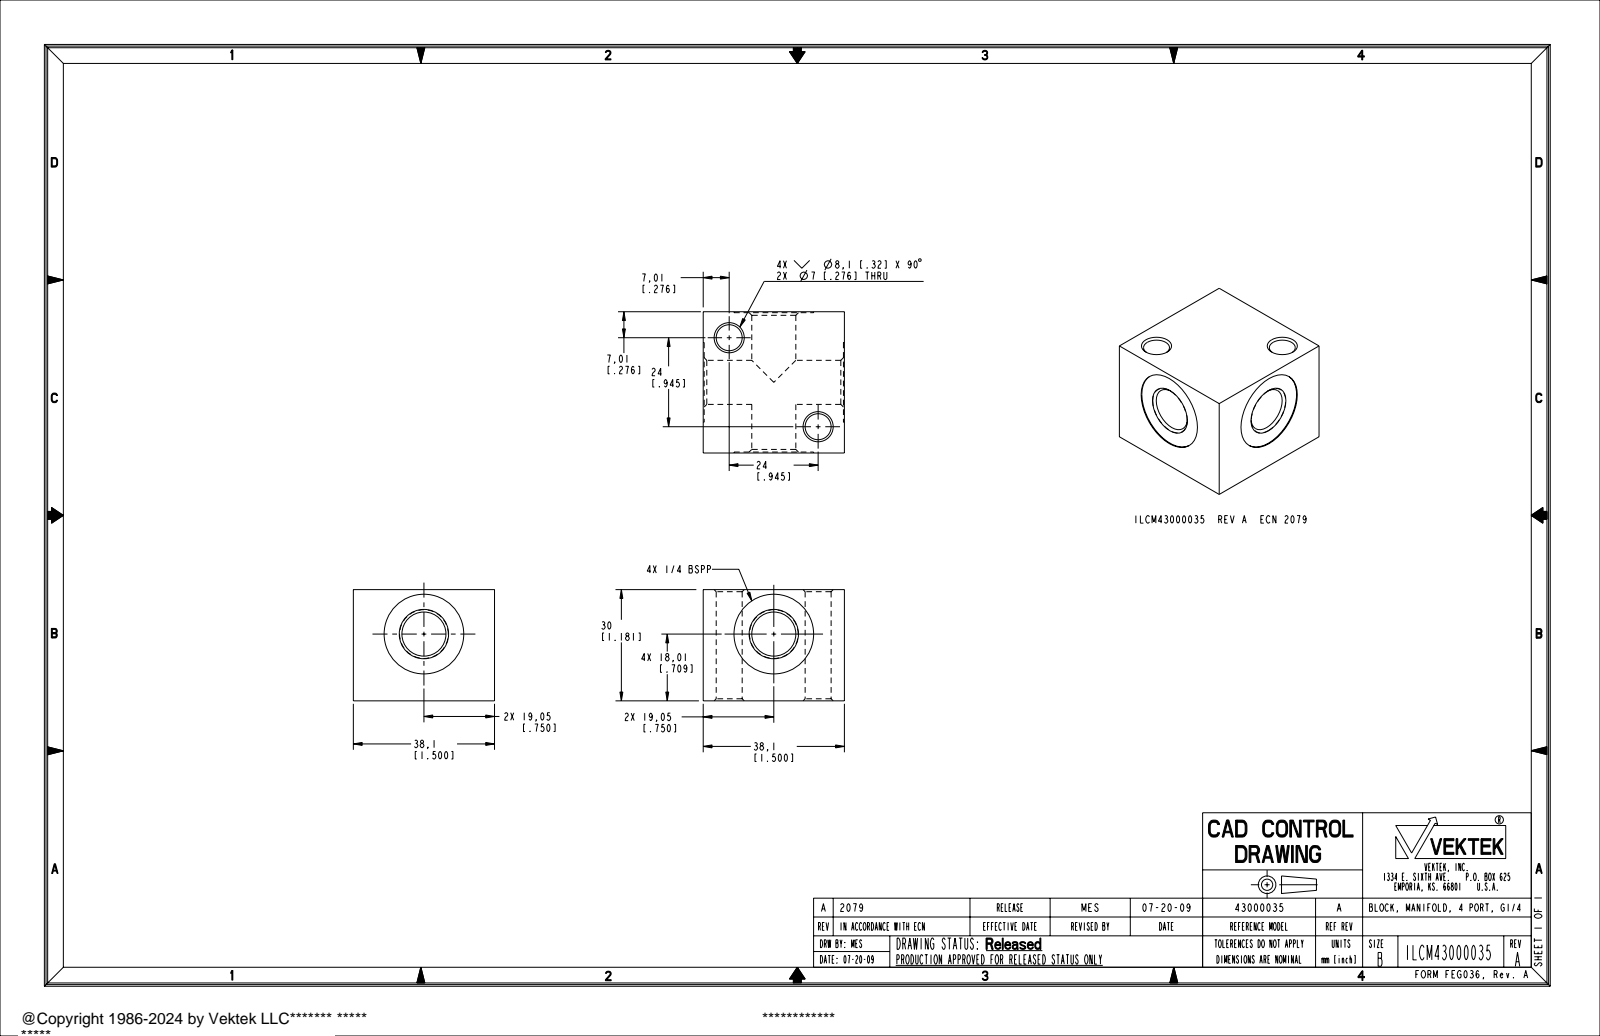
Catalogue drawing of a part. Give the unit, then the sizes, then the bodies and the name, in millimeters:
Units: millimetres
Overall size (bounding box): 38.1 × 38.1 × 30
Round holes (diameter × count): ⌀7 ×2, ⌀11.9 ×2, ⌀21.5 ×2
Round bosses / shafts (diameter × count): ⌀13.2 ×2
Main face-to-face distances: 38.1, 30, 37.8, 37.6, 26.8, 26.6, 11.3, 11, 15.6
Hole centre spacings: 33.9
Volume: 33 580 mm³ · Surface area: 12 340 mm²
Bodies: 1 solid, 58 faces (14 planar, 28 cylindrical, 16 other)
Part name (STEP PRODUCT): ILCM43000035
STEP written by: PRO/ENGINEER BY PARAMETRIC TECHNOLOGY CORPORATION, 2007460 (AUTOMOTIVE_DESIGN_CC2)
